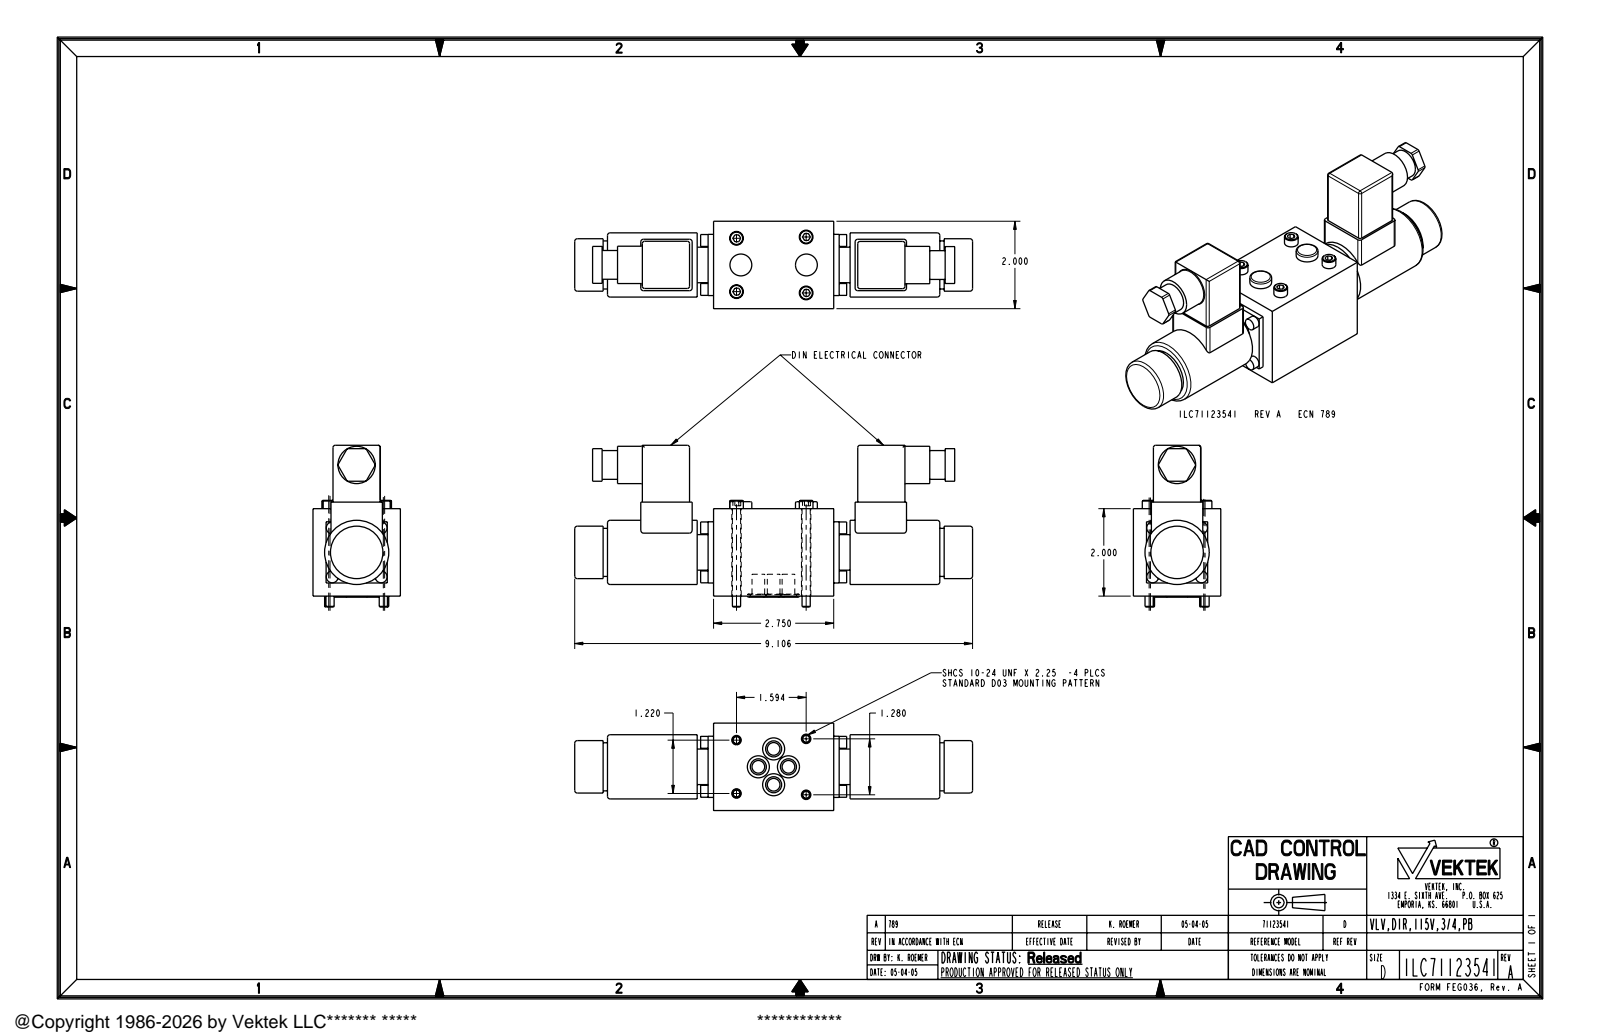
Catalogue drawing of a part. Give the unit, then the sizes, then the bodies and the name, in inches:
Units: inches
Overall size (bounding box): 9.106 × 3.7 × 2
Round holes (diameter × count): ⌀0.215 ×4, ⌀0.29 ×4, ⌀0.49 ×4
Round bosses / shafts (diameter × count): ⌀0.313 ×4, ⌀0.272 ×4, ⌀0.187 ×4, ⌀0.854 ×2, ⌀0.658 ×2, ⌀0.5 ×2, ⌀1.469 ×1, ⌀1.2 ×1
Partial cylindrical surfaces — rounded edges, fillets, slot ends (radius × count): R0.05 ×26, R0.06 ×8
Main face-to-face distances: 2, 1.08, 0.412, 1.588, 0.55, 0.125, 0.458, 0.462, 1.538, 1.542
Hole centre spacings: 0.532, 0.539, 0.757, 0.779, 0.789, 0.873, 1.268, 1.287
Volume: 25.88 in³ · Surface area: 100.3 in²
Bodies: 1 solid, 282 faces (120 planar, 118 cylindrical, 44 other)
Part name (STEP PRODUCT): ILC71123541
STEP written by: PRO/ENGINEER BY PARAMETRIC TECHNOLOGY CORPORATION, 2004290 (AUTOMOTIVE_DESIGN_CC2)
